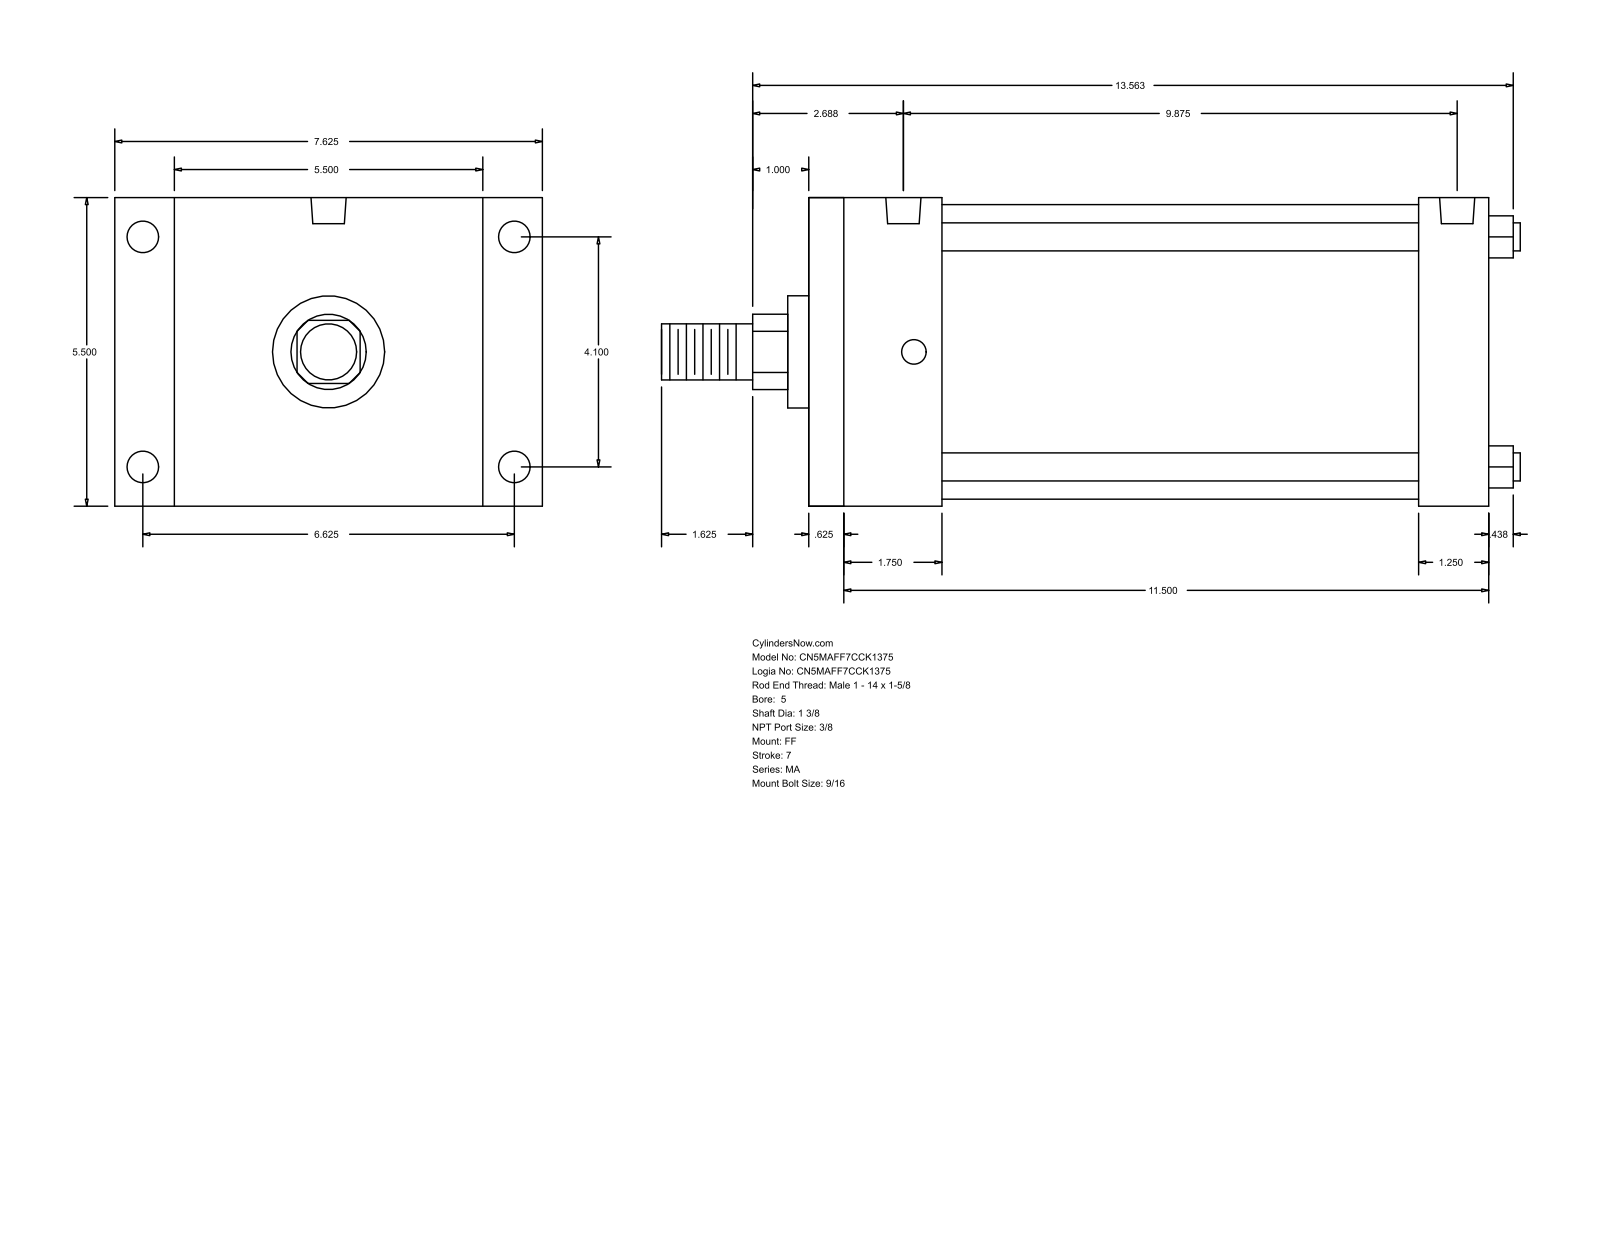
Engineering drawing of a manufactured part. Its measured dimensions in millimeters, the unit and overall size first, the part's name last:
Units: millimetres
Overall size (bounding box): 388.94 × 193.68 × 139.7
Round holes (diameter × count): ⌀11.11 ×4, ⌀14.29 ×4, ⌀15.93 ×2
Round bosses / shafts (diameter × count): ⌀12.7 ×4, ⌀133.35 ×1, ⌀50.8 ×1, ⌀34.92 ×1, ⌀25.4 ×1
Partial cylindrical surfaces — rounded edges, fillets, slot ends (radius × count): R17.06 ×1
Main face-to-face distances: 139.7, 307.98, 15.87, 292.11, 276.22, 260.35, 31.76, 60.32, 44.45, 215.9
Hole centre spacings: 4.77, 104.14, 168.28, 197.9, 241.29, 246.06, 250.83
Bodies: 0 solids, 92 faces (64 planar, 28 cylindrical, 0 other)
Part name (STEP PRODUCT): MA_FF__0500_1.375
STEP written by: GSSL Pune (CONFIG_CONTROL_DESIGN)
